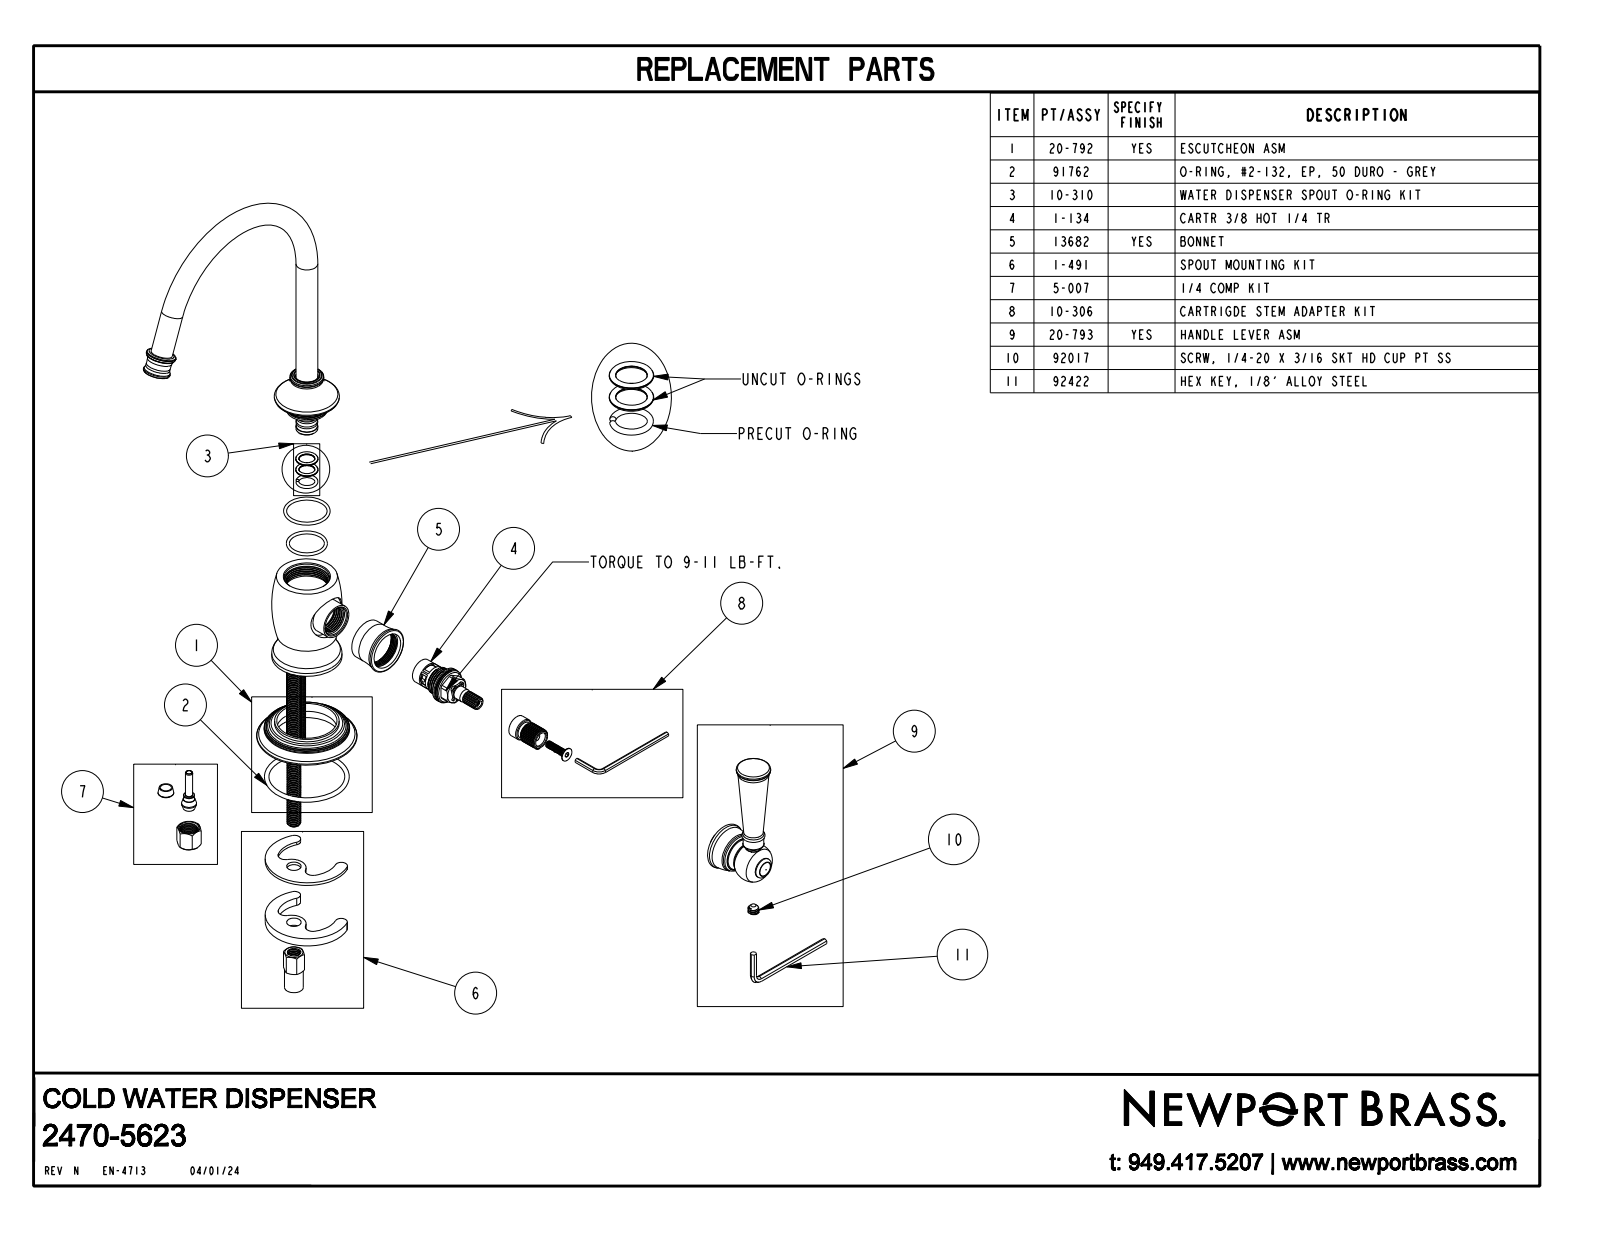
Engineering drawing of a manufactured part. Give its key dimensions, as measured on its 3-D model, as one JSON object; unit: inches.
{"part_name": "2470-5623", "step_written_by": "CREO PARAMETRIC BY PTC INC, 2018400 (CONFIG_CONTROL_DESIGN)", "units": "inches", "bodies": {"solids": 1, "faces": 165, "planar": 13, "cylindrical": 20, "other": 132}, "overall_size": [9.404, 6.184, 3.825], "volume_in3": 9.715, "surface_area_in2": 50.85, "round_holes": [[1, 1]], "round_bosses_or_shafts": [[0.5, 3], [1.61, 1], [0.95, 1], [0.785, 1], [0.48, 1], [0.335, 1], [0.33, 1]], "face_to_face_distances": [0.021, 3.214, 0.374, 2.84, 0.44, 0.701, 0.68, 2.267, 1.893, 0.947]}
